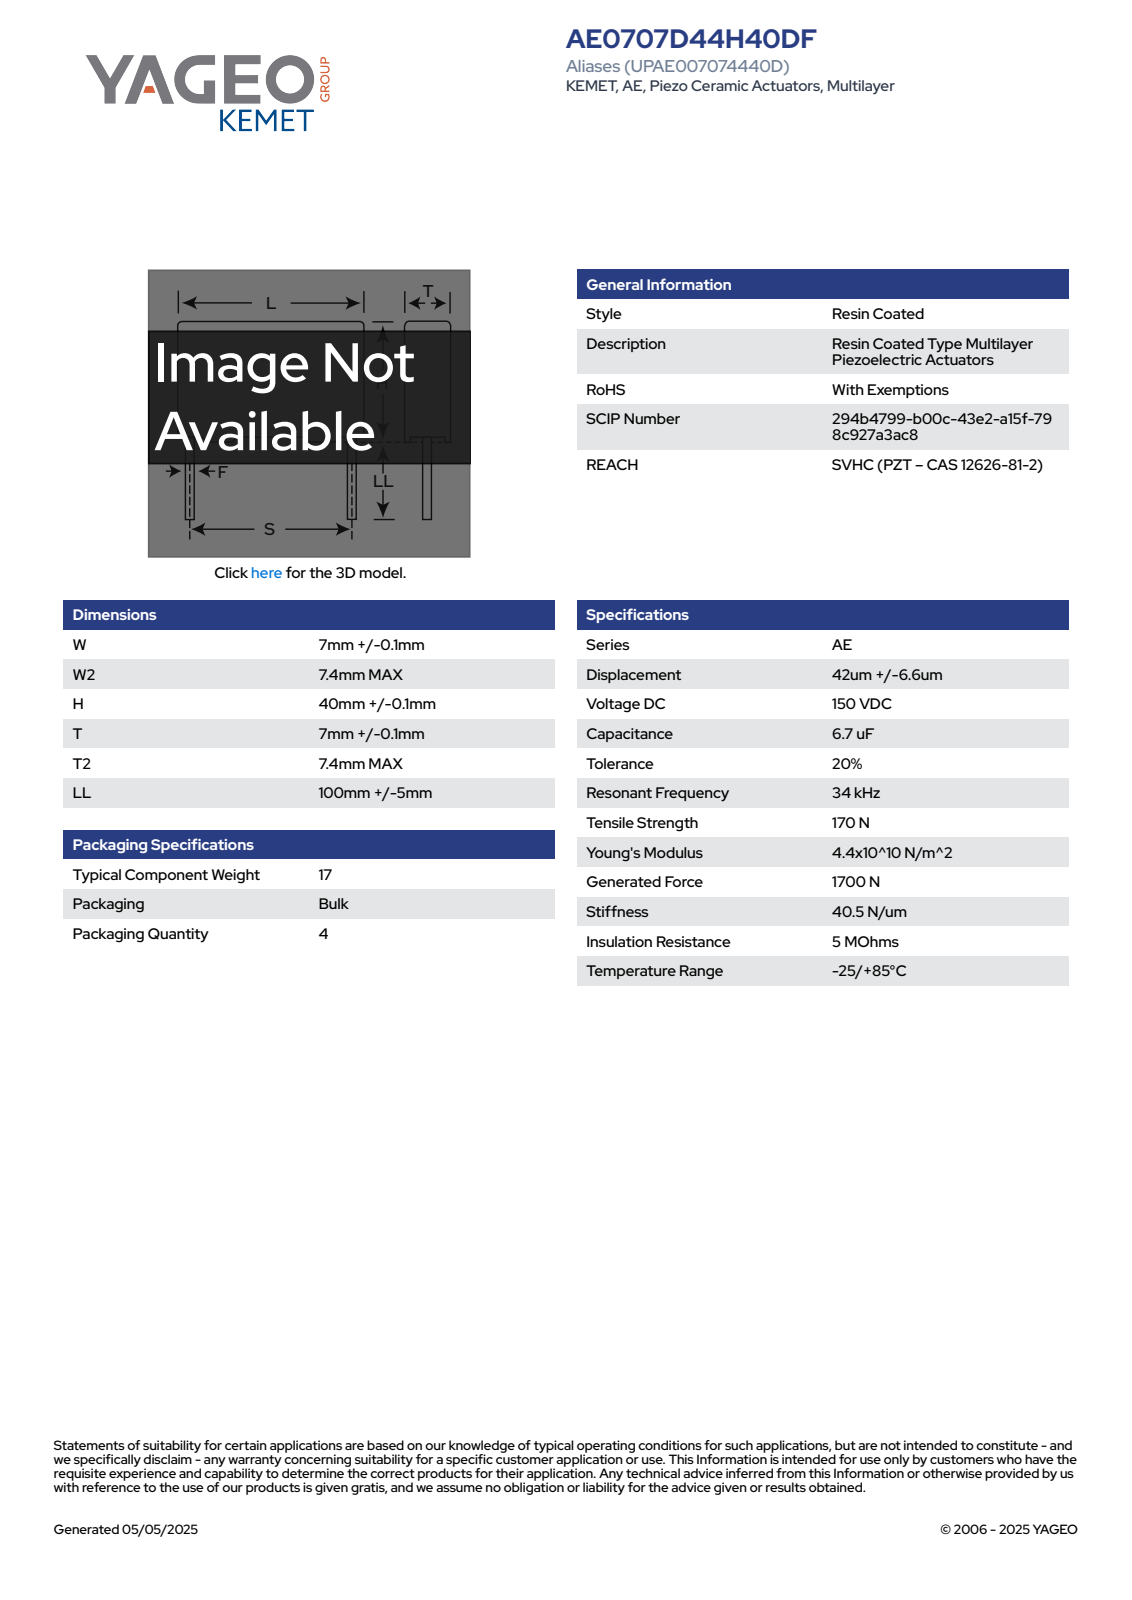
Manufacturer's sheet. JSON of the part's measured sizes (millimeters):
{"part_name": "AL_KAE1_W7.1W27.4H40.1T7.1T27.4", "step_written_by": "SolidWorks 2014 (AUTOMOTIVE_DESIGN)", "units": "millimeters", "bodies": {"solids": 4, "faces": 93, "planar": 85, "cylindrical": 8, "other": 0}, "overall_size": [40.1, 7.4, 7.4], "volume_mm3": 2021, "surface_area_mm2": 1264, "partial_cylinders_radius": [[0.15, 8]], "face_to_face_distances": [7.1, 7, 7.25, 6.9, 7.4, 40.1, 16.12, 23.98, 3.93, 36.17]}
